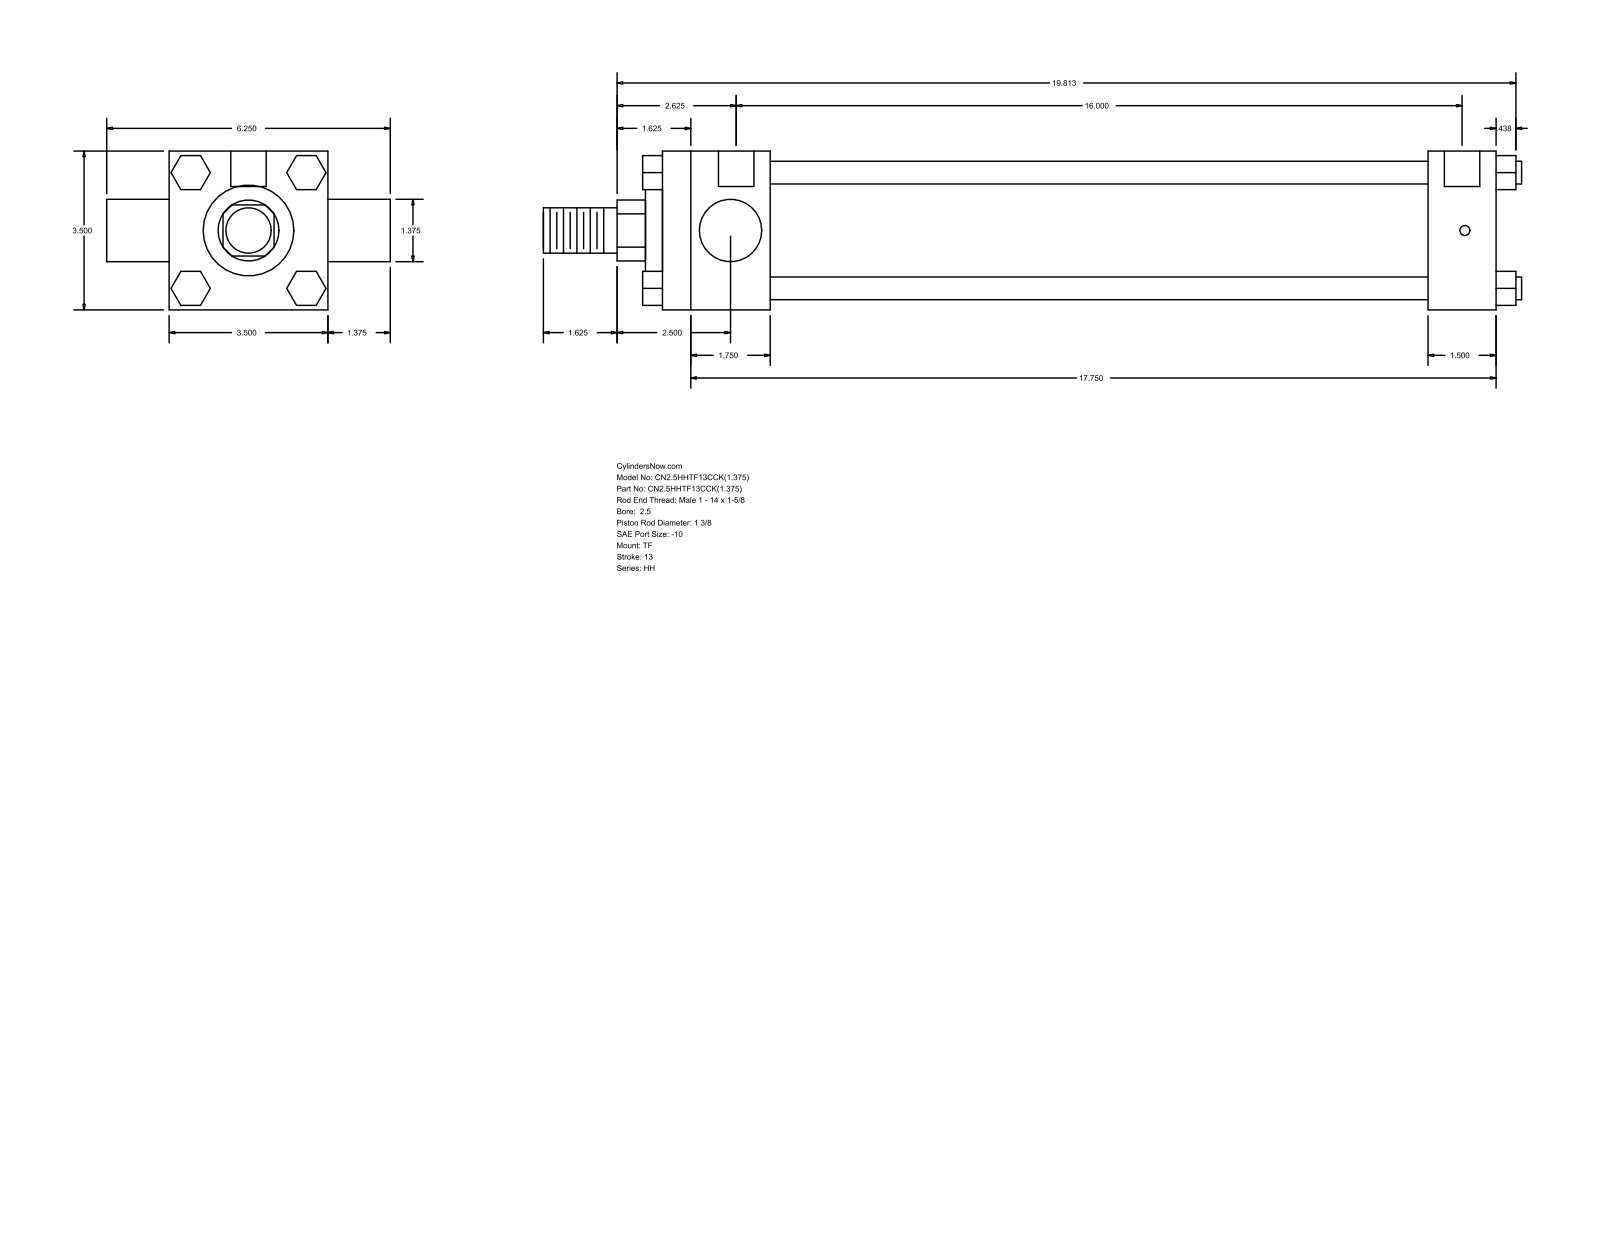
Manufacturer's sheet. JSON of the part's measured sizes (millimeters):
{"part_name": "HH_TF__0250_1.375", "step_written_by": "GSSL Pune (CONFIG_CONTROL_DESIGN)", "units": "millimeters", "bodies": {"solids": 0, "faces": 120, "planar": 92, "cylindrical": 28, "other": 0}, "overall_size": [547.69, 158.75, 88.9], "round_holes": [[5.56, 3], [19.84, 2]], "round_bosses_or_shafts": [[12.7, 4], [34.92, 2], [73.03, 1], [50.8, 1], [25.4, 1]], "partial_cylinders_radius": [[17.06, 1]], "face_to_face_distances": [88.9, 466.72, 60.32, 406.4, 428.62, 368.3, 38.1, 19.05, 32.38, 56.09], "hole_center_spacings": [1.58, 1.59, 406.4, 407.98, 407.99, 409.57]}
